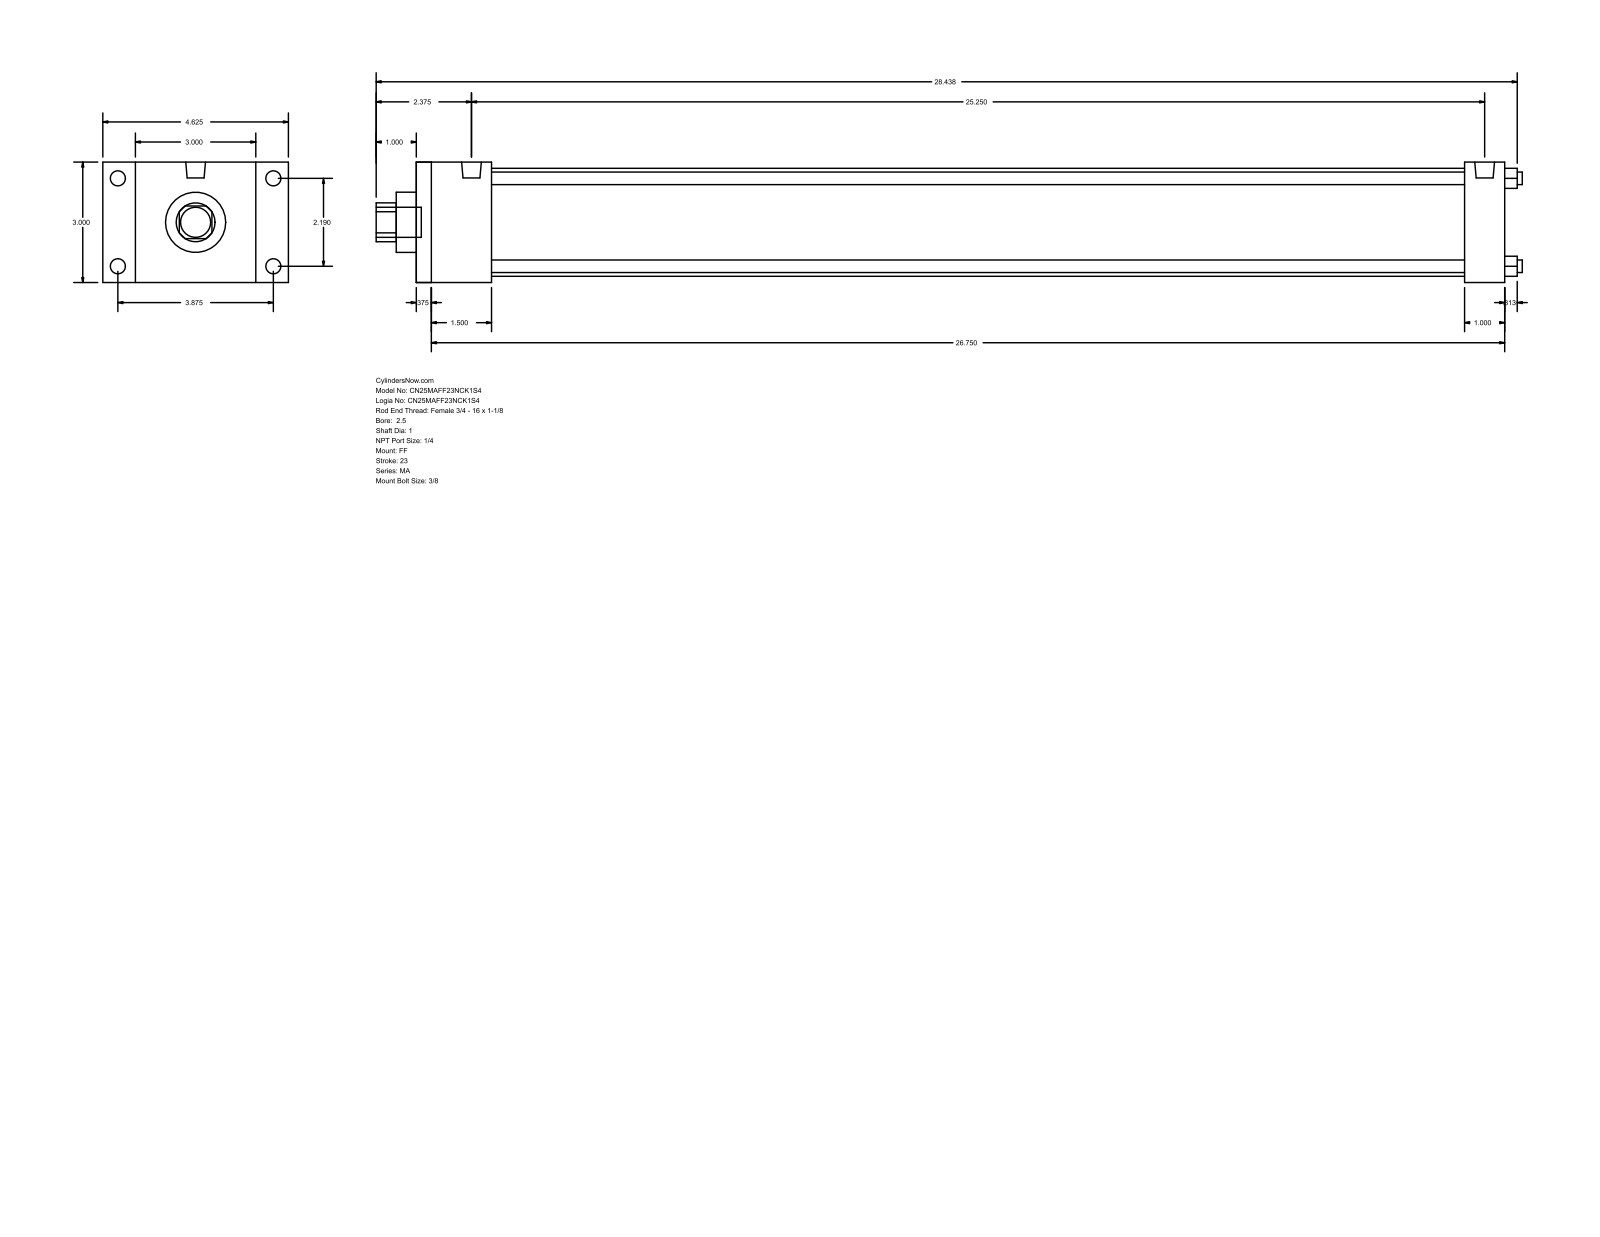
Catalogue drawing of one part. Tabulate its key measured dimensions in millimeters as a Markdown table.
| quantity | value |
| --- | --- |
| part name | MA_FF__0250_1 |
| STEP written by | GSSL Pune (CONFIG_CONTROL_DESIGN) |
| units | millimeters |
| bodies | 0 solids, 92 faces (64 planar, 28 cylindrical, 0 other) |
| overall size | 725.49 × 117.47 × 76.2 |
| round holes (diameter × count) | 7.94 × 4, 25.4 × 1, 38.1 × 1, 68.33 × 1 |
| round bosses / shafts (diameter × count) | 9.53 × 4, 7.94 × 4, 12.49 × 2, 19.05 × 1 |
| partial cylindrical surfaces (radius × count) | 12.29 × 1 |
| main face-to-face distances | 76.2, 688.98, 9.52, 679.46, 25.4, 47.63, 663.58, 38.11, 654.06, 615.95 |
| hole center spacings | 39.33, 55.62, 78.66 |
